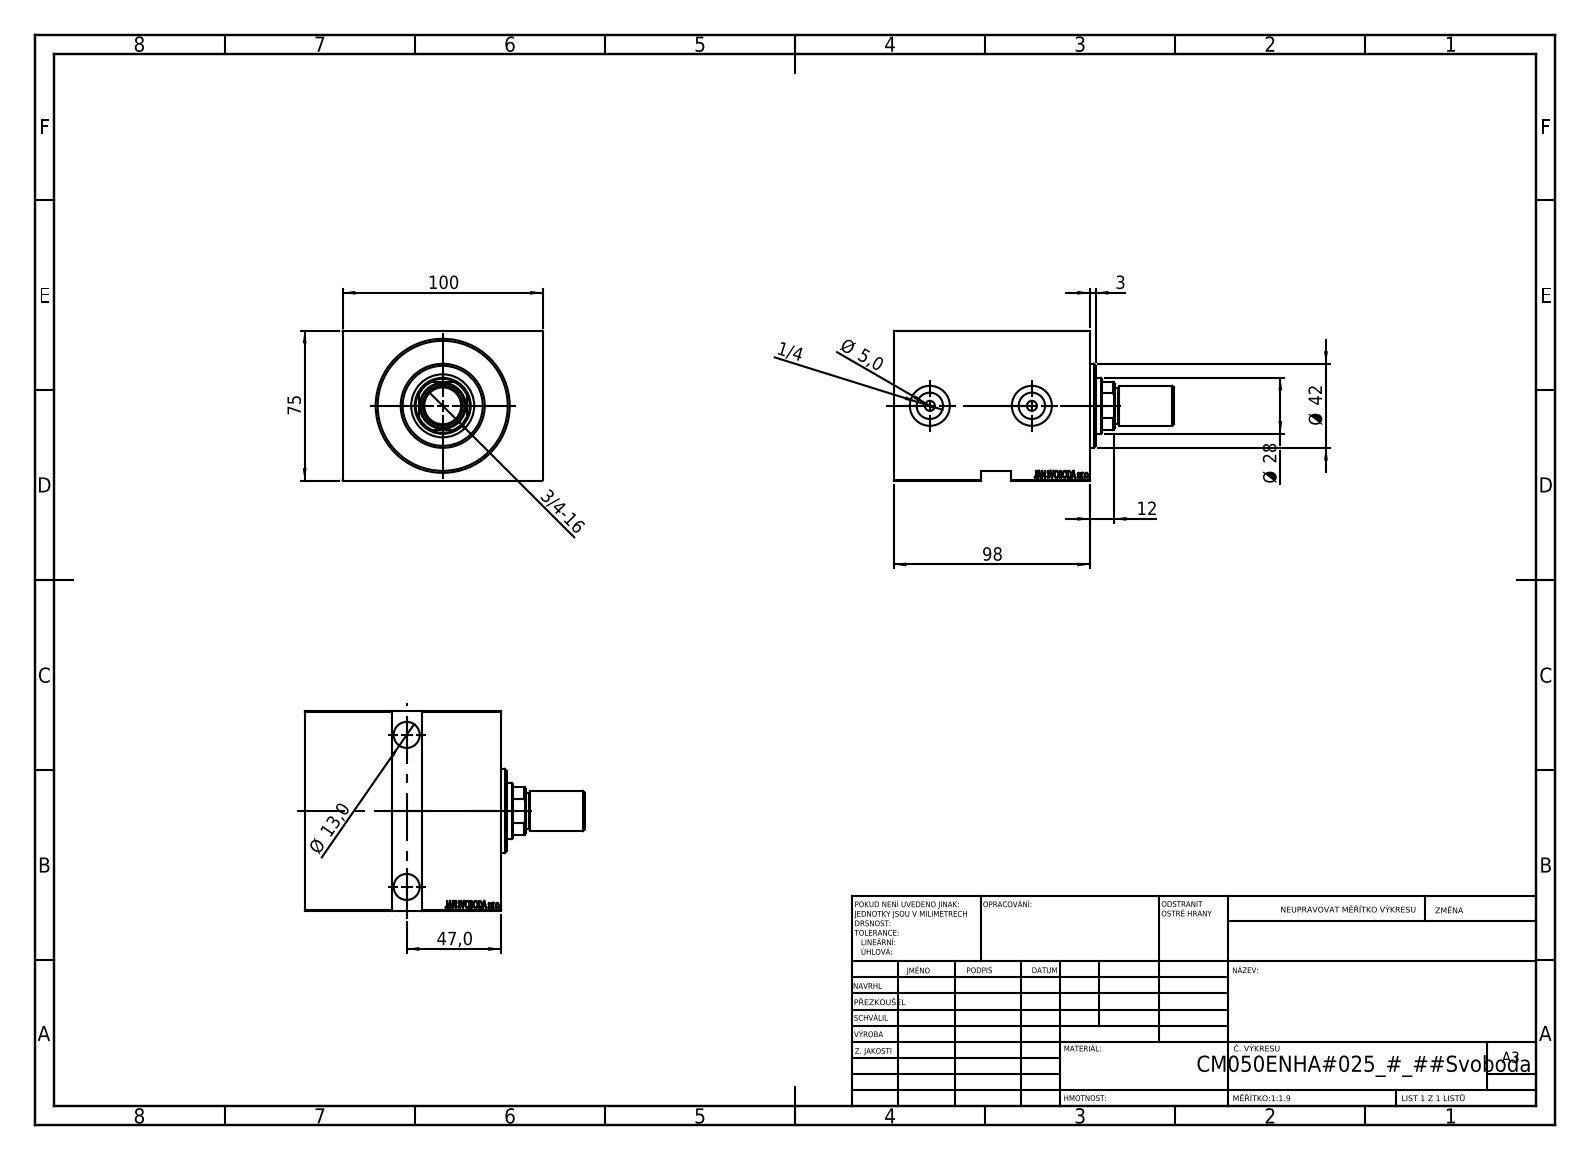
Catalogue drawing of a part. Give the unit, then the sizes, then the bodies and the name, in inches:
Units: inches
Overall size (bounding box): 5.512 × 3.937 × 2.953
Round holes (diameter × count): ⌀0.197 ×2, ⌀0.512 ×2, ⌀0.518 ×2, ⌀0.748 ×2, ⌀0.787 ×2, ⌀0.728 ×1, ⌀1.102 ×1, ⌀1.24 ×1, ⌀1.969 ×1, ⌀2.559 ×1
Round bosses / shafts (diameter × count): ⌀2.047 ×1, ⌀1.654 ×1, ⌀0.787 ×1, ⌀0.709 ×1
Partial cylindrical surfaces — rounded edges, fillets, slot ends (radius × count): R0.531 ×1
Main face-to-face distances: 2.953, 3.937, 3.858, 0.551, 3.307, 0.197, 3.11, 3.661, 1.85, 3.205
Hole centre spacings: 2.008, 2.992
Volume: 41.7 in³ · Surface area: 156.8 in²
Bodies: 4 solids, 860 faces (412 planar, 48 cylindrical, 400 other)
Part name (STEP PRODUCT): V450CM_VC_B; V450CM_E_Body; V450CM_E_VCP; V450CM_MALE_METRIC
STEP written by: SolidWorks 2019 (CONFIG_CONTROL_DESIGN)
